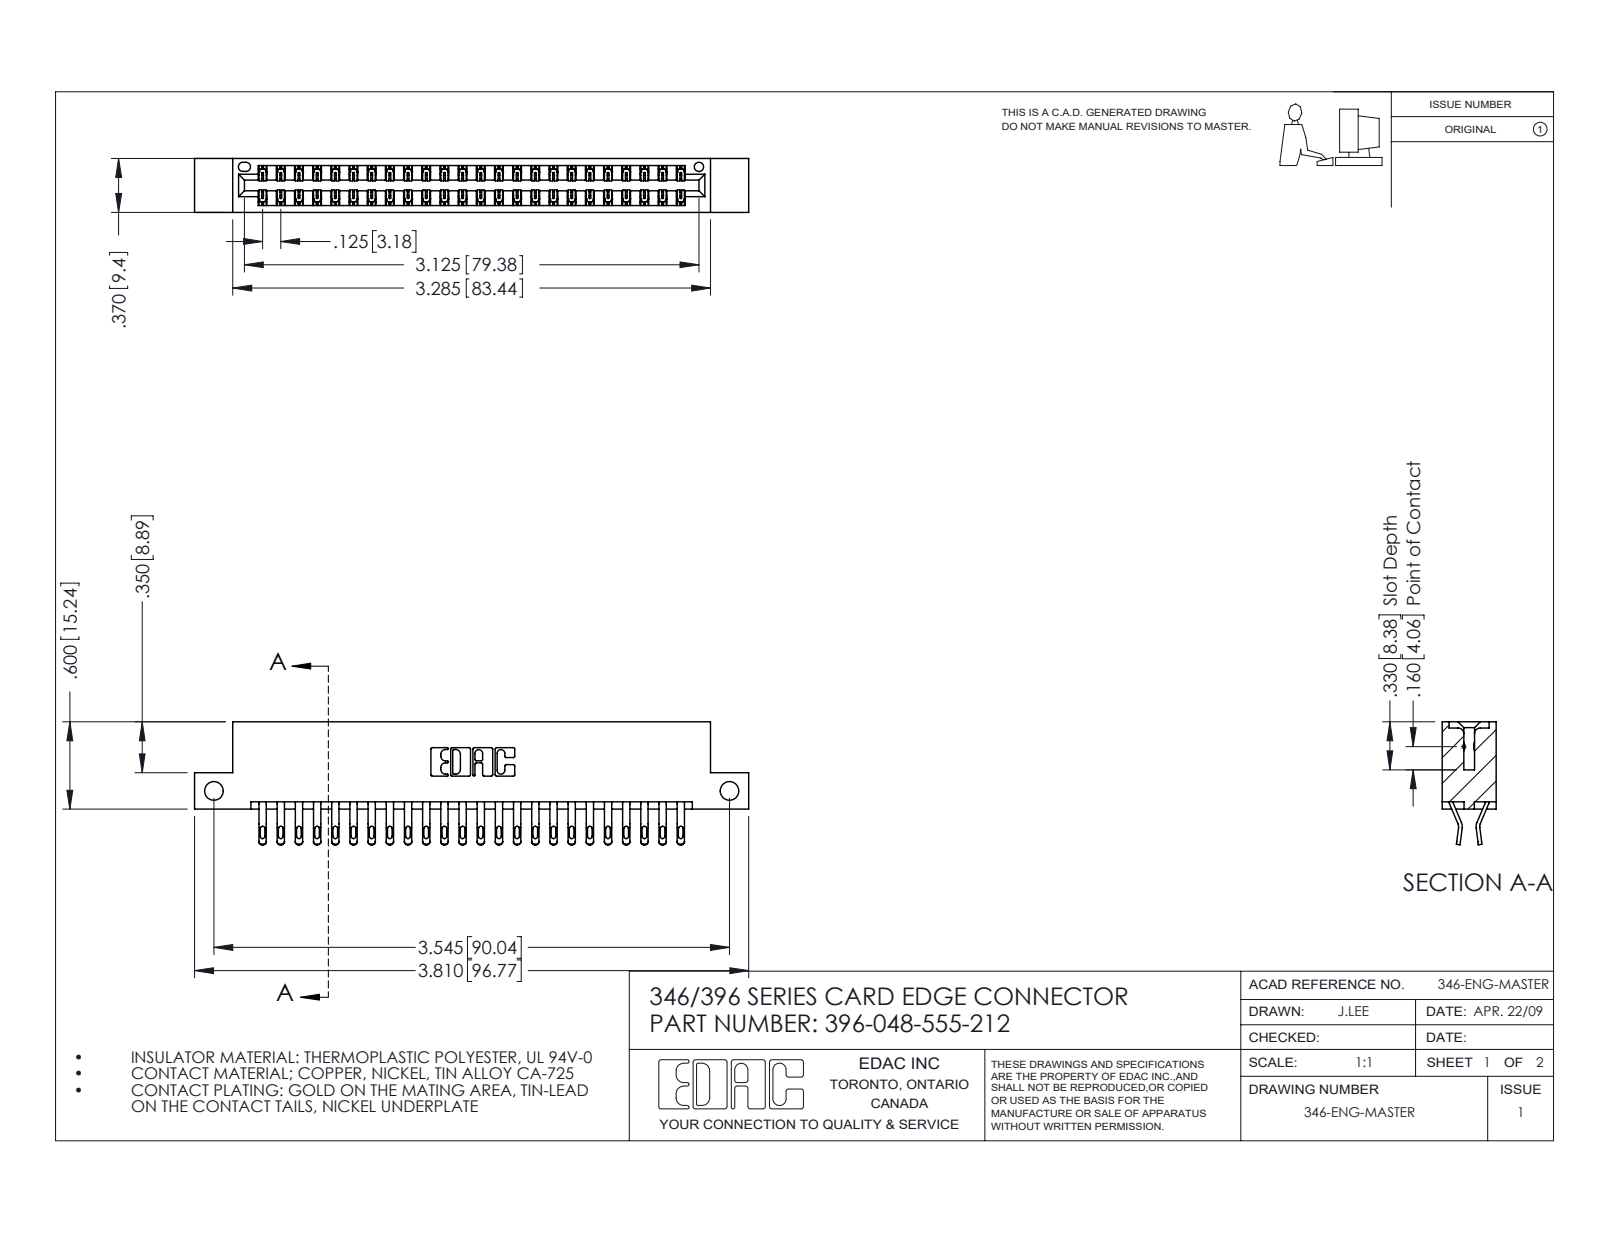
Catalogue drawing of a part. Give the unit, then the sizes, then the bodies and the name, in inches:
Units: inches
Overall size (bounding box): 3.81 × 0.845 × 0.37
Round holes (diameter × count): ⌀0.128 ×2, ⌀0.064 ×1
Partial cylindrical surfaces — rounded edges, fillets, slot ends (radius × count): R0.016 ×96, R0.02 ×96, R0.006 ×72, R0.01 ×22, R0.007 ×6, R0.031 ×6, R0.026 ×3, R0.01 ×2
Main face-to-face distances: 0.048, 0.322, 0.25, 0.37, 0.025, 0.072, 0.298, 0.275, 0.148, 0.222
Hole centre spacings: 3.545
Volume: 0.57 in³ · Surface area: 20.04 in²
Bodies: 49 solids, 2906 faces (1660 planar, 1246 cylindrical, 0 other)
Part name (STEP PRODUCT): 396-048-555-212; 345-292-001_555 Tail; 346 Part_Flush Mounting Lugs - Side Mount
STEP written by: SolidWorks 2016 (CONFIG_CONTROL_DESIGN)
